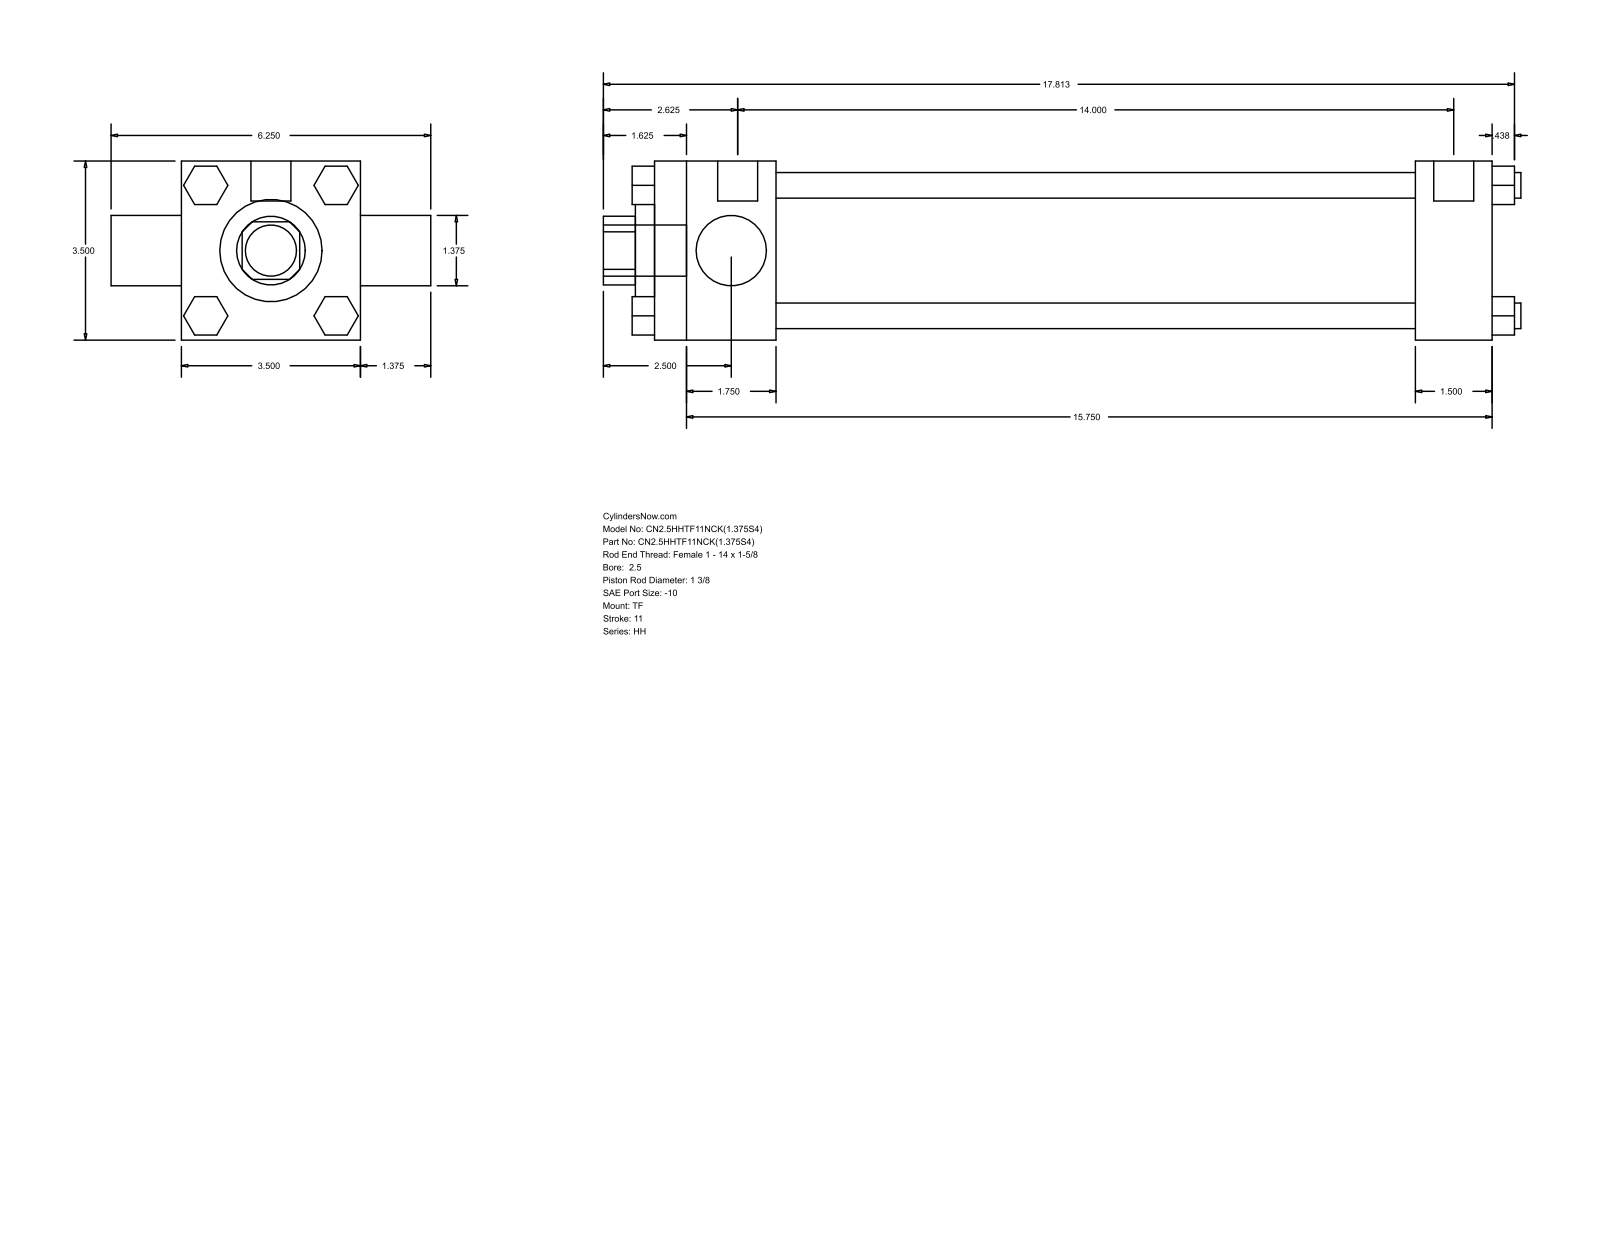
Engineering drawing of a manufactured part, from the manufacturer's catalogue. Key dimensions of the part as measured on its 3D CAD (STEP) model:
Part name (STEP PRODUCT): HH_TF__0250_1.375
STEP written by: GSSL Pune (CONFIG_CONTROL_DESIGN)
Units: millimetres
Bodies: 0 solids, 120 faces (92 planar, 28 cylindrical, 0 other)
Overall size (bounding box): 455.61 × 158.75 × 88.9
Round holes (diameter × count): ⌀34.92 ×2, ⌀50.8 ×1, ⌀73.03 ×1
Round bosses / shafts (diameter × count): ⌀12.7 ×4, ⌀5.56 ×3, ⌀19.84 ×2, ⌀25.4 ×1
Partial cylindrical surfaces — rounded edges, fillets, slot ends (radius × count): R17.06 ×1
Main face-to-face distances: 88.9, 415.92, 60.32, 355.6, 377.83, 317.51, 38.09, 19.05, 32.38, 56.09
